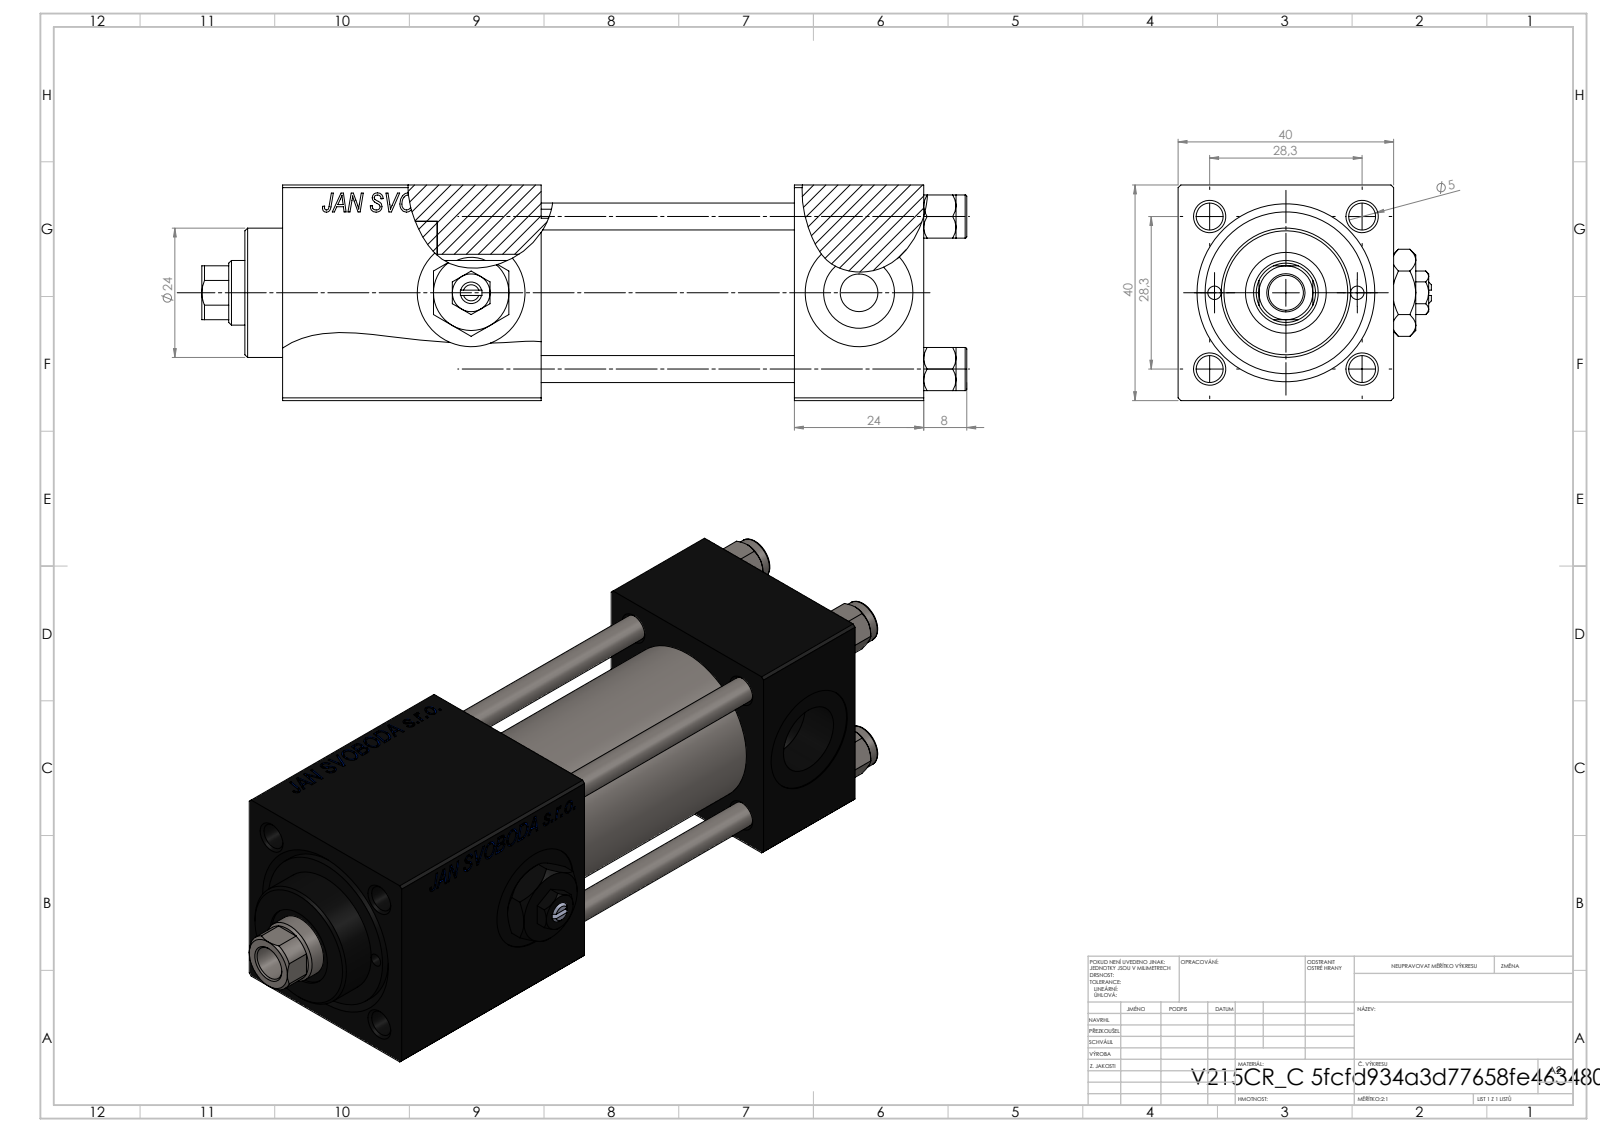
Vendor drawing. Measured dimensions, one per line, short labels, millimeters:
name: V215CR_VCP_C; NUT_M5_C; V215_VC_A; V215CR_C_TYCINKA (+2 more)
written by: SolidWorks 2019 (CONFIG_CONTROL_DESIGN)
unit: mm
bodies: 12 solids, 1201 faces (551 planar, 94 cylindrical, 556 other)
size: 142 × 47 × 40
volume: 141 941 mm³; area: 55 199 mm²
holes: 4× ⌀5, 3× ⌀20, 2× ⌀2.5, 2× ⌀7, 2× ⌀13.16, 1× ⌀6.5, 1× ⌀12, 1× ⌀15, 1× ⌀25, 1× ⌀30
bosses: 4× ⌀8, 1× ⌀31, 1× ⌀24
rounds: 1× R5.5
face distances: 40, 24, 90.3, 66.3, 48, 47, 71, 19.3, 119, 95
hole spacings: 14.18, 20.01, 28.3, 30.84, 13.25, 40.02, 26.5, 72
